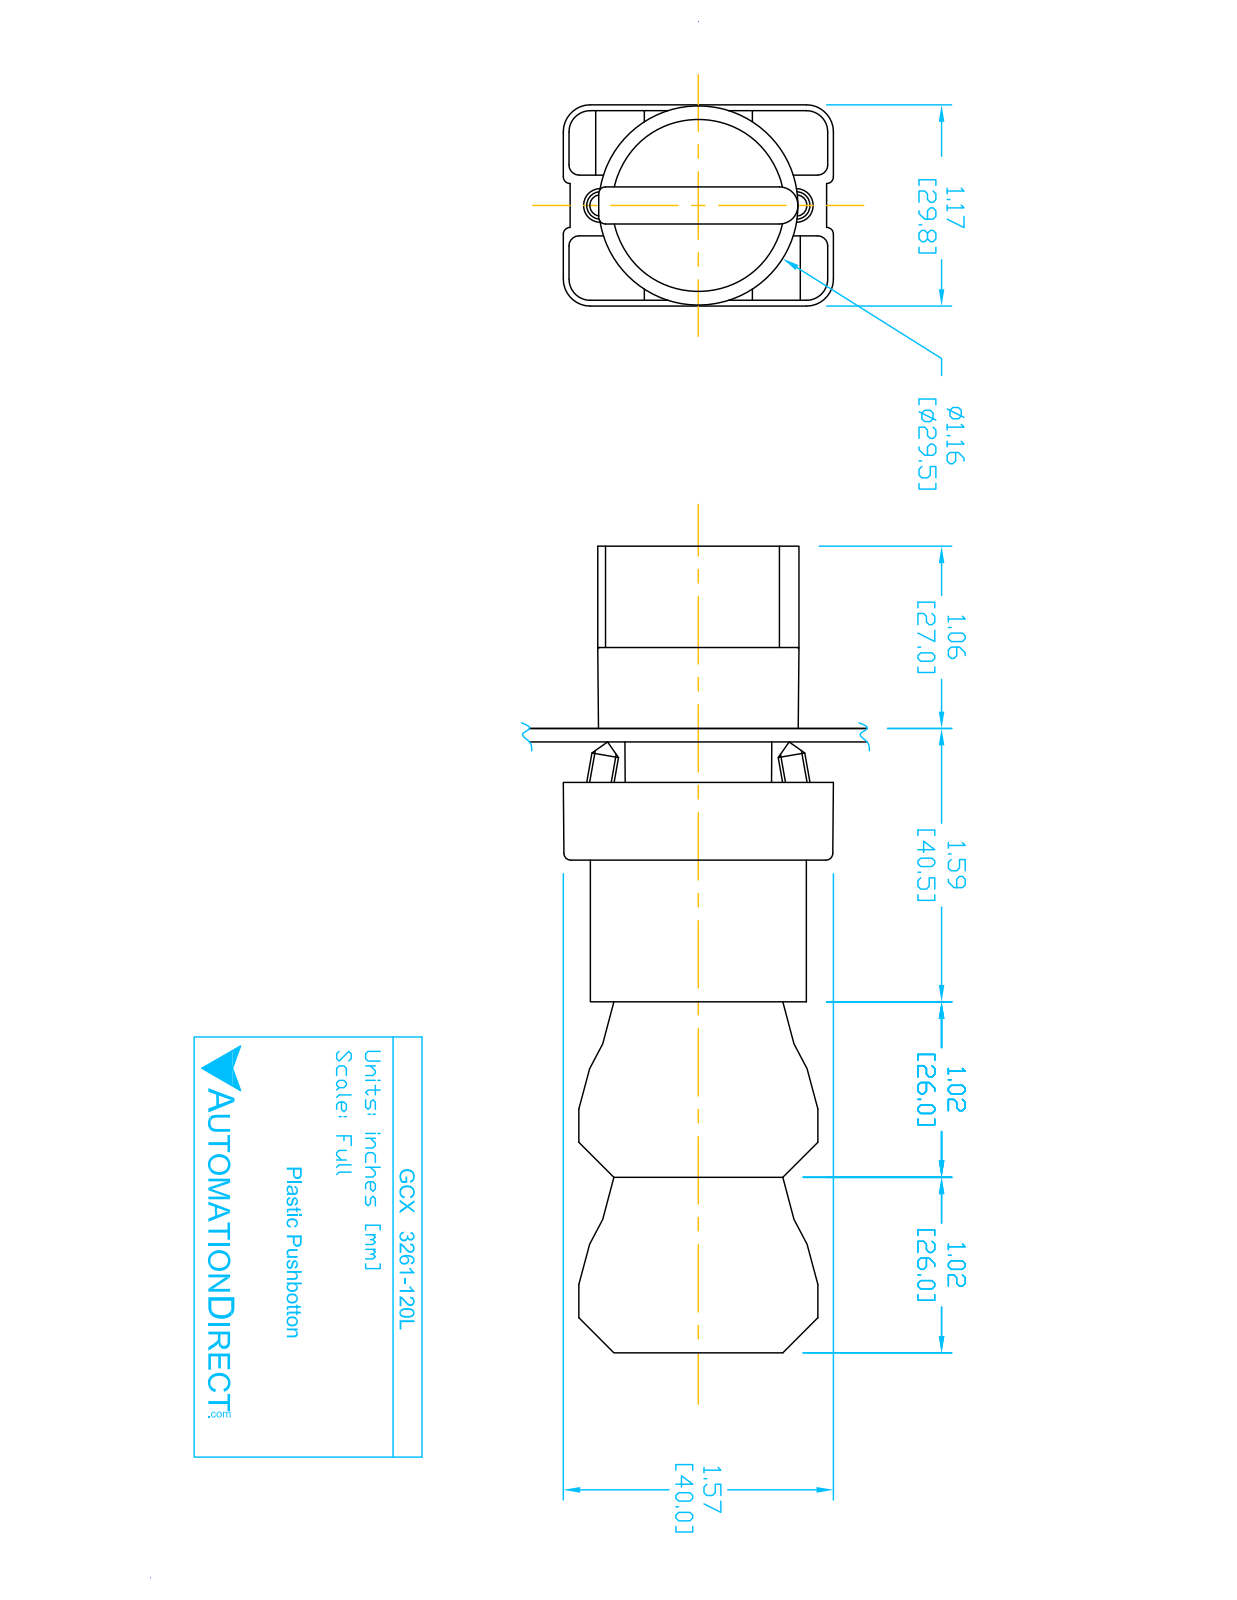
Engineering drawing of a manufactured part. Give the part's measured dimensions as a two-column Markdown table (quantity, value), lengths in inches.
| quantity | value |
| --- | --- |
| part name | ecx1040; GCX3261L OPERATOR; ecx1030; ECX1050 (+2 more) |
| STEP written by | SolidWorks 2016 (AUTOMOTIVE_DESIGN) |
| units | inches |
| bodies | 11 solids, 724 faces (488 planar, 193 cylindrical, 43 other) |
| overall size | 4.677 × 1.581 × 1.177 |
| volume | 4.751 in³ |
| surface area | 59.22 in² |
| round holes (diameter × count) | 0.079 × 4, 0.087 × 2, 0.124 × 2, 0.13 × 2, 0.197 × 1, 0.469 × 1, 0.878 × 1, 0.888 × 1, 1.024 × 1 |
| round bosses / shafts (diameter × count) | 0.157 × 4, 1.175 × 1, 1.004 × 1, 0.945 × 1, 0.856 × 1, 0.78 × 1, 0.504 × 1 |
| partial cylindrical surfaces (radius × count) | 0.059 × 24, 0.041 × 12, 0.124 × 12, 0.157 × 12, 0.039 × 9, 0.02 × 2, 0.063 × 2, 0.079 × 2 |
| main face-to-face distances | 0.579, 0.593, 1.024, 1.171, 0.014, 0.827, 1.85, 3.043, 2.02, 1.193 |
| hole center spacings | 0.236, 1.003, 0.974, 0.472, 0.539, 0.544, 1.083, 0.484 |
